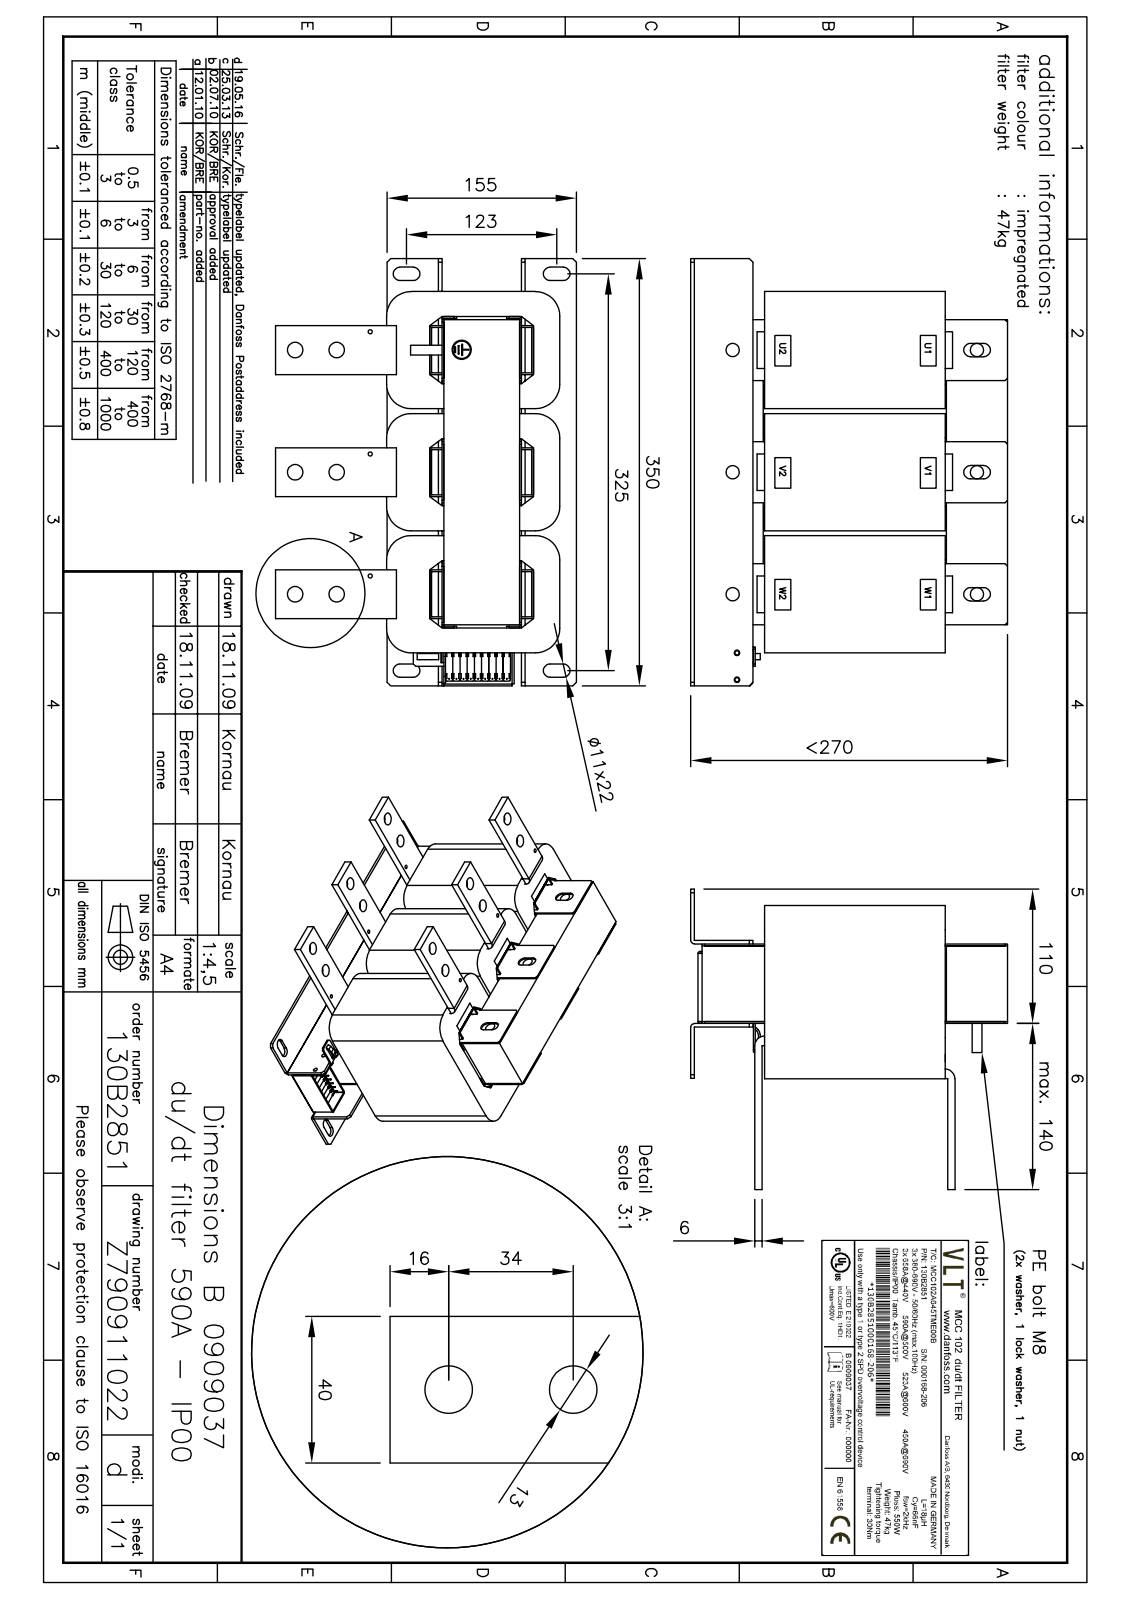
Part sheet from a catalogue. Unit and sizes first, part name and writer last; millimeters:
Units: millimetres
Overall size (bounding box): 350 × 268.3 × 234.5
Round holes (diameter × count): ⌀3.7 ×6, ⌀6.8 ×6, ⌀8 ×6, ⌀8.4 ×6, ⌀11 ×6, ⌀13 ×6, ⌀4.1 ×5, ⌀4.3 ×5, ⌀4.5 ×4, ⌀4 ×2, ⌀5.76 ×1, ⌀8.1 ×1
Round bosses / shafts (diameter × count): ⌀24 ×6, ⌀16 ×6, ⌀13 ×6, ⌀9 ×5, ⌀8 ×5, ⌀7.6 ×5, ⌀4 ×3, ⌀6 ×2
Partial cylindrical surfaces — rounded edges, fillets, slot ends (radius × count): R5.5 ×22, R0.1 ×19, R1.1 ×12, R20 ×12, R1.6 ×5, R4 ×4, R1 ×2, R6.1 ×2
Main face-to-face distances: 1, 2, 62.5, 32, 100, 34, 24, 76, 64, 98
Hole centre spacings: 100, 31.32, 63.3, 200, 89.34, 104.92, 105.62, 118.24
Volume: 8 022 000 mm³ · Surface area: 1 356 000 mm²
Bodies: 93 solids, 1450 faces (975 planar, 225 cylindrical, 250 other)
Part name (STEP PRODUCT): #700-1264; #700-1265; curved spring lock washer_din_Spring washer DIN 128 - A4; Wickel B 0909037 (+8 more)
STEP written by: SolidWorks 2014 (AUTOMOTIVE_DESIGN)
